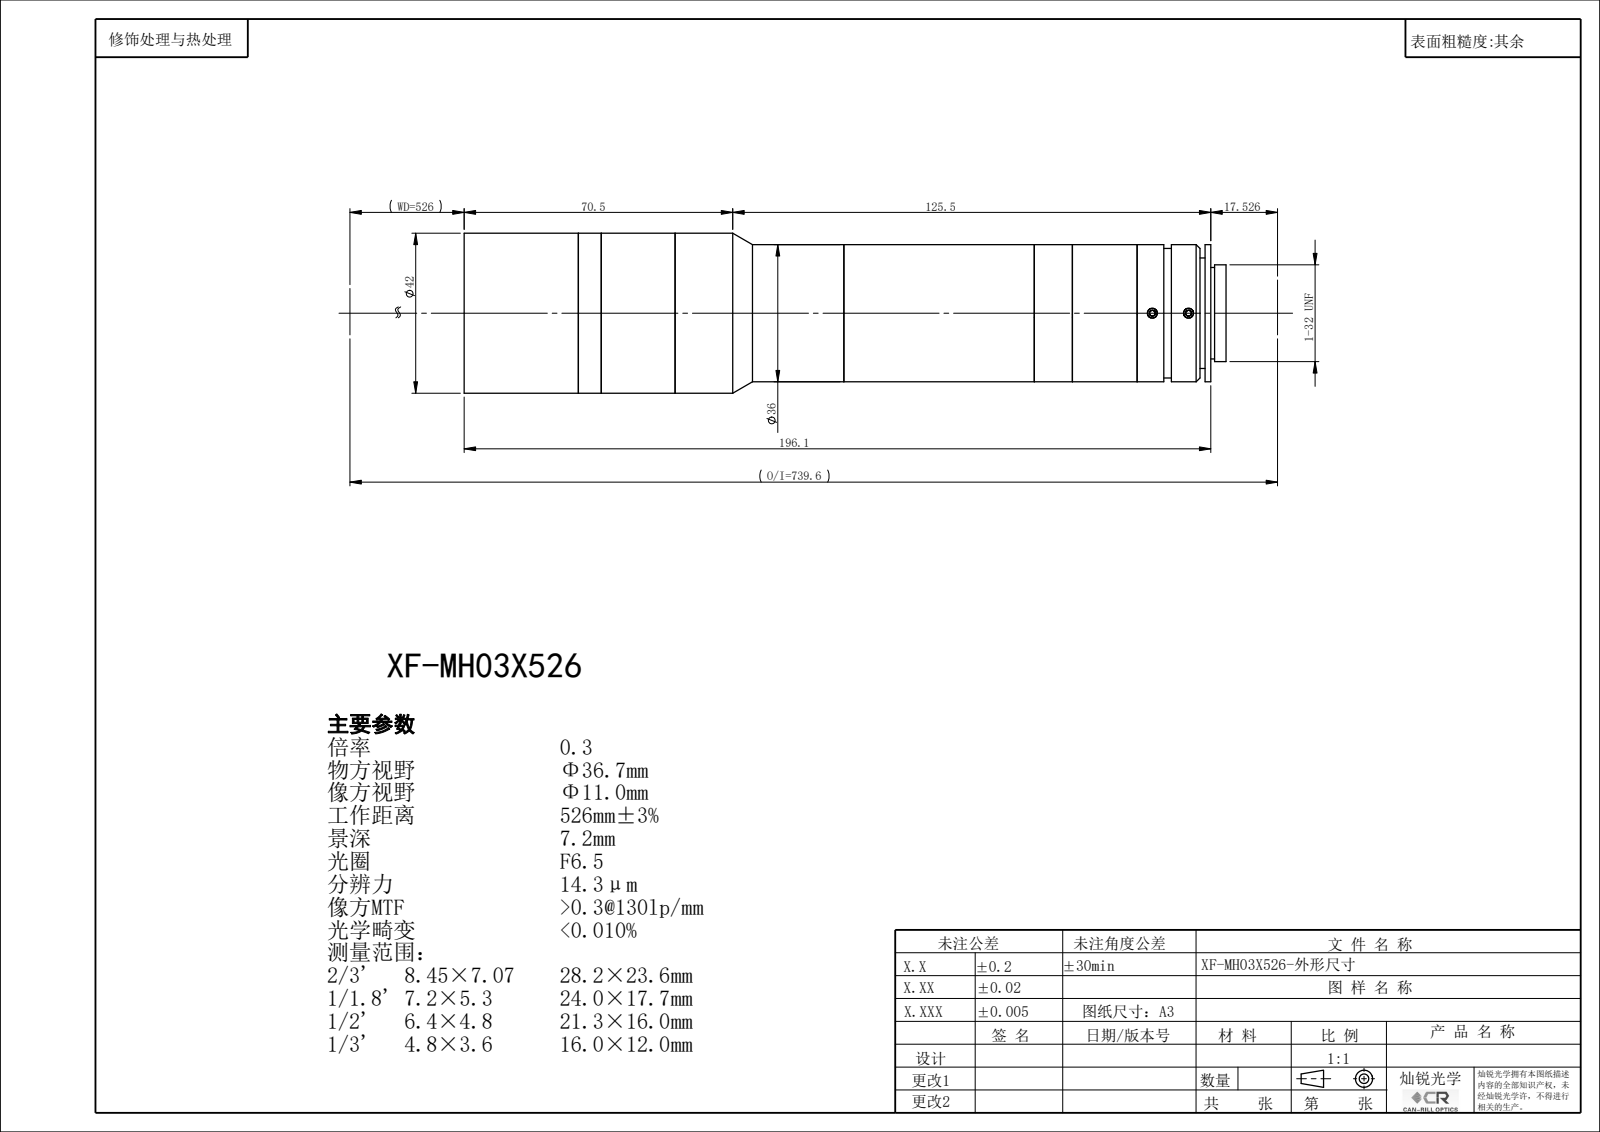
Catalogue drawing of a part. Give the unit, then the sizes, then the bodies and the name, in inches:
Units: inches
Overall size (bounding box): 7.883 × 1.654 × 1.654
Round holes (diameter × count): ⌀0.098 ×3, ⌀0.827 ×1, ⌀1.299 ×1, ⌀1.433 ×1
Round bosses / shafts (diameter × count): ⌀1.654 ×1, ⌀1.417 ×1, ⌀1.102 ×1, ⌀1 ×1, ⌀0.177 ×1
Partial cylindrical surfaces — rounded edges, fillets, slot ends (radius × count): R0.984 ×5, R0.098 ×1, R0.826 ×1
Main face-to-face distances: 0.276, 0.315, 0.039, 0.394, 0.433, 0.236, 0.591, 0.157, 7.292, 7.331
Bodies: 0 solids, 131 faces (40 planar, 67 cylindrical, 24 other)
Part name (STEP PRODUCT): XF-MH03X526
STEP written by: SolidWorks 2014 (CONFIG_CONTROL_DESIGN)
